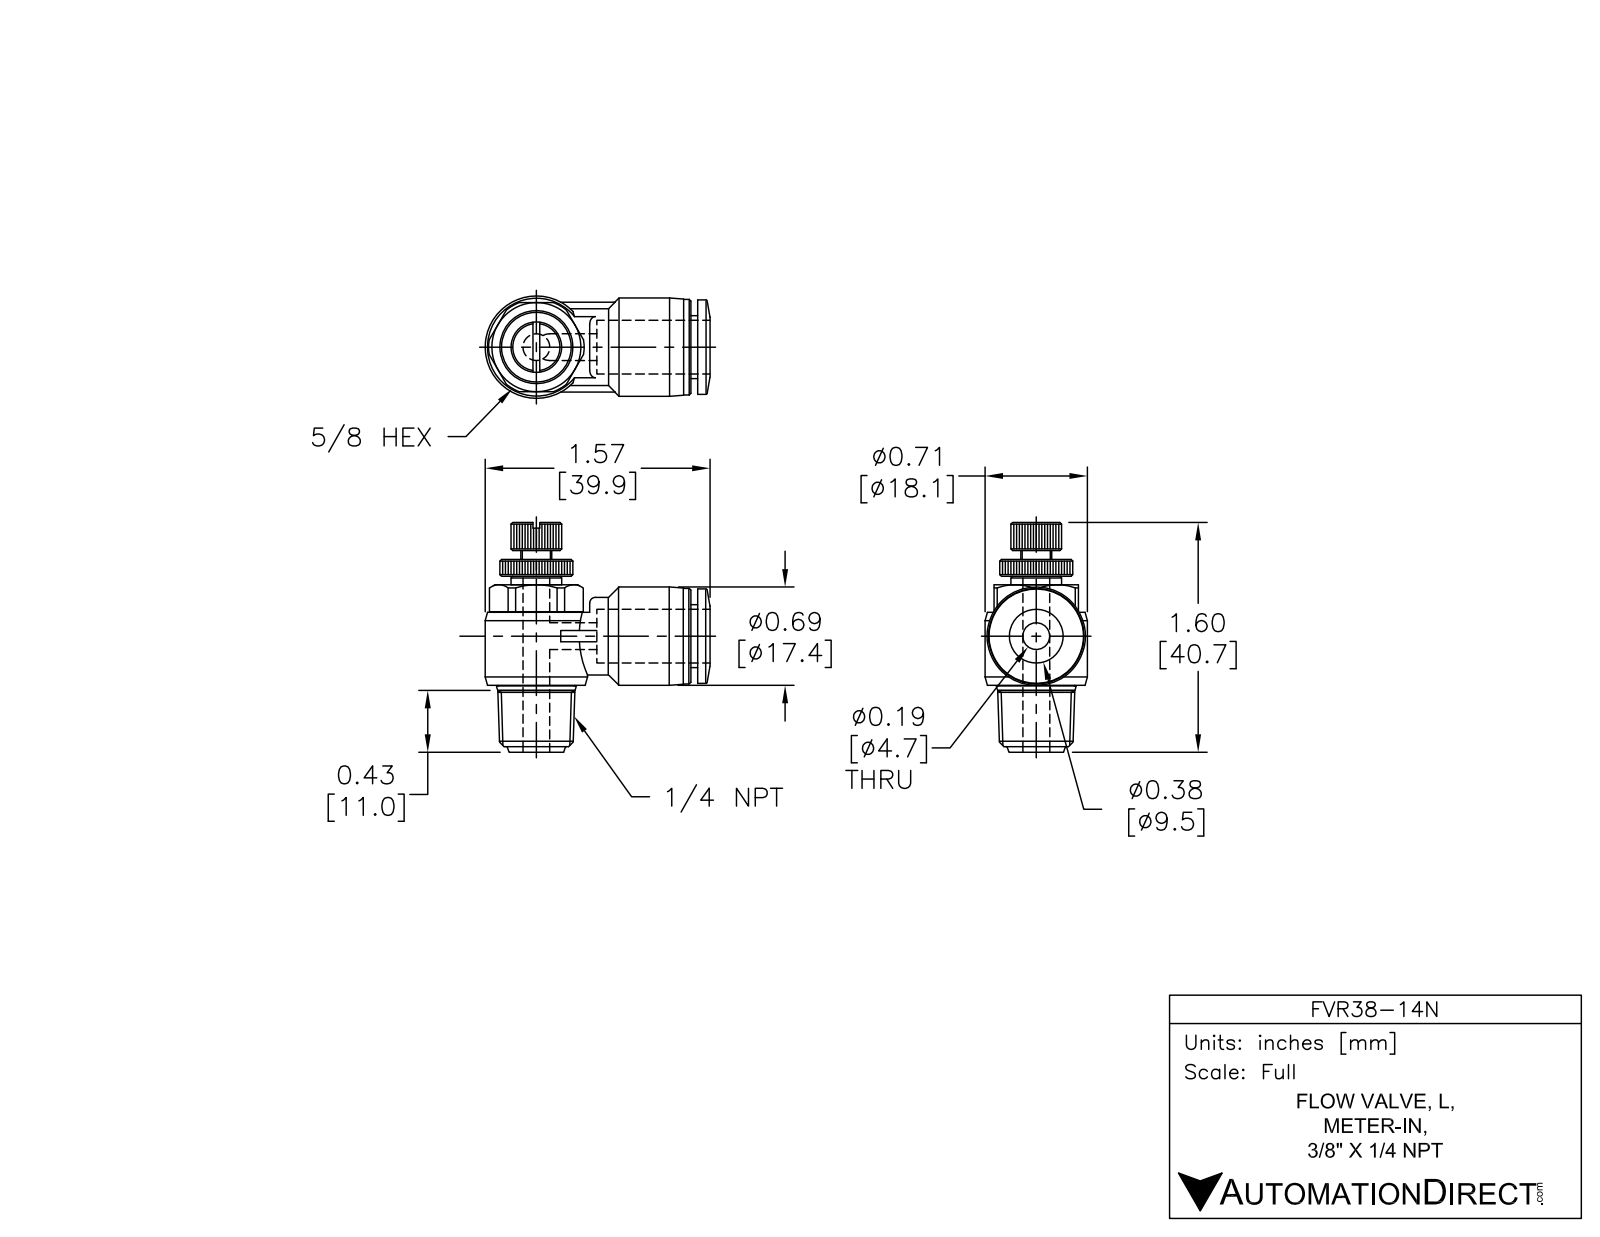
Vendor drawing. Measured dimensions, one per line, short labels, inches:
name: FVR38-14N
written by: SolidWorks 2015 (AUTOMOTIVE_DESIGN)
unit: in
bodies: 1 solid, 427 faces (188 planar, 113 cylindrical, 126 other)
size: 1.85 × 1.575 × 0.717
volume: 0.586 in³; area: 8.222 in²
holes: 2× ⌀0.177, 1× ⌀0.386
bosses: 1× ⌀0.717, 1× ⌀0.689, 1× ⌀0.669, 1× ⌀0.661, 1× ⌀0.591, 1× ⌀0.543, 1× ⌀0.539, 1× ⌀0.441
rounds: 1× R0.256, 1× R0.335
face distances: 0.705, 0.047, 0.177, 0.882, 0.624, 0.512, 0.193, 0.37, 0.764, 0.252
